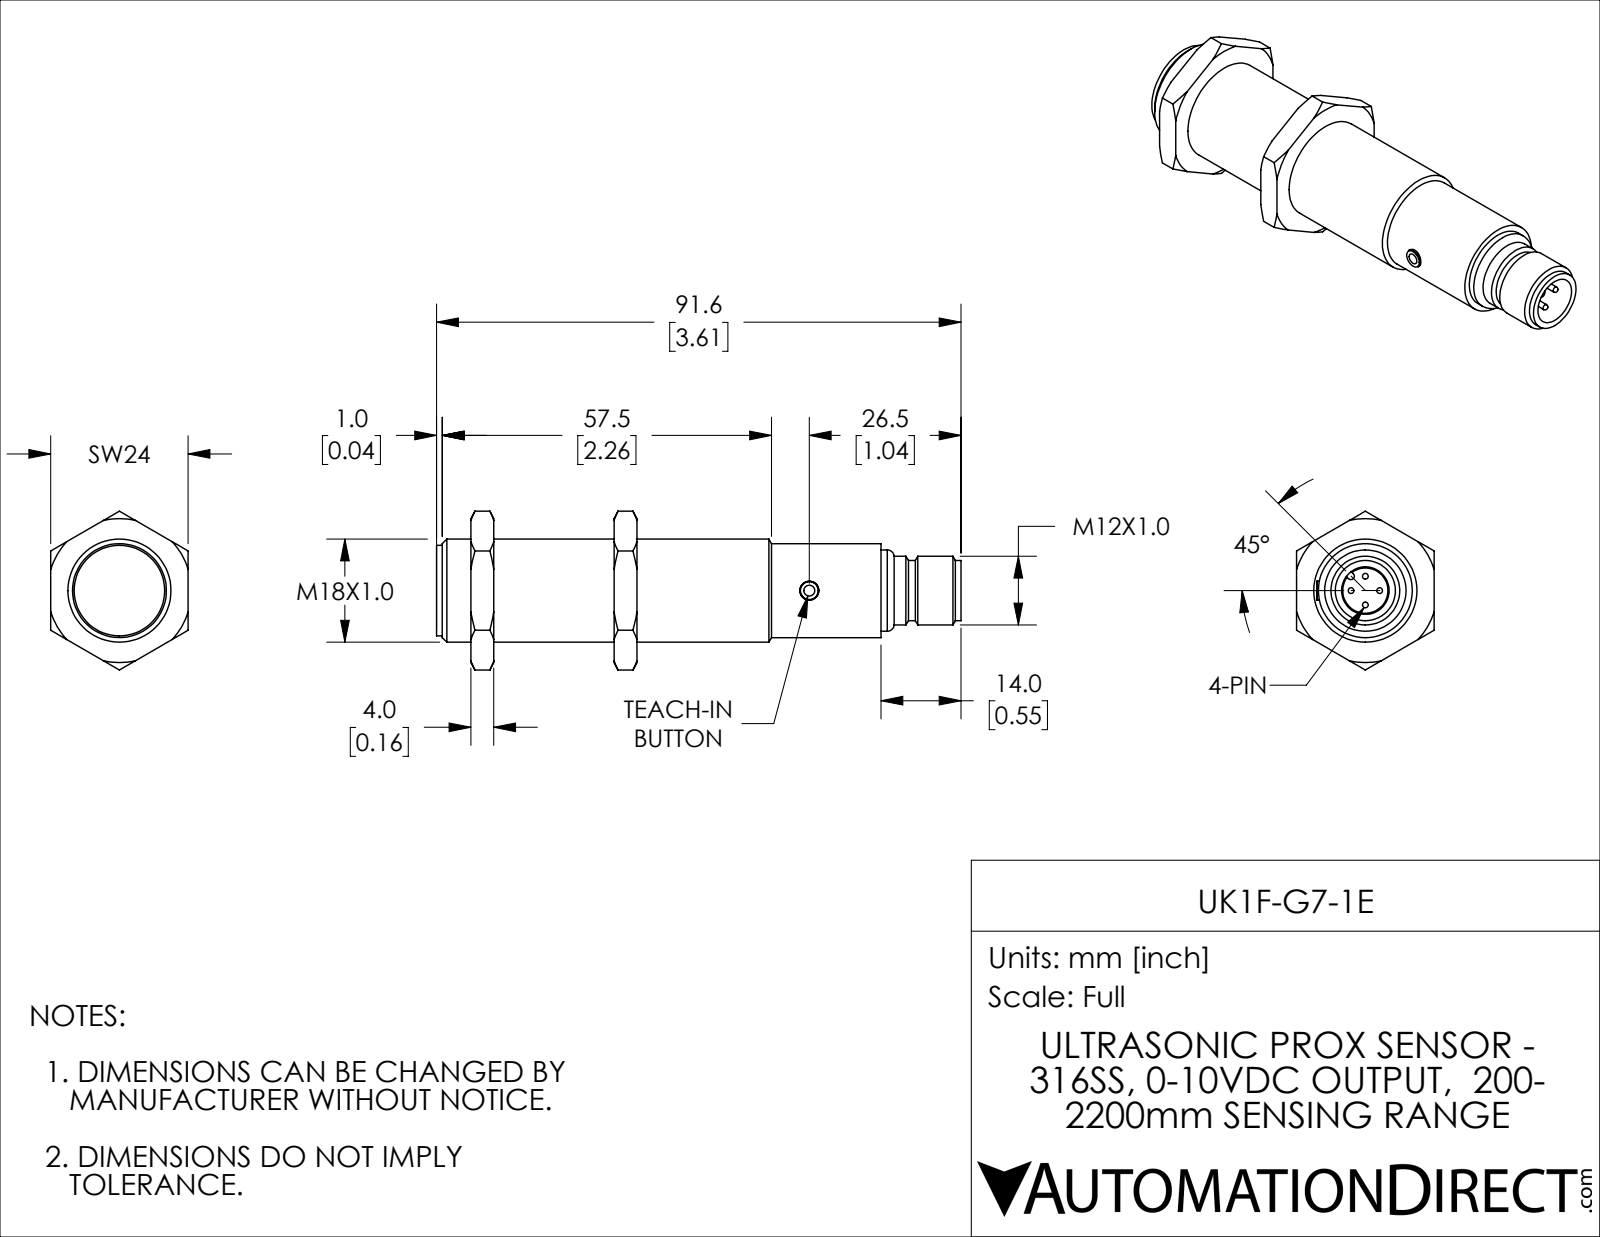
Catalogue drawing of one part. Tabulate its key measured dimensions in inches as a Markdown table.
| quantity | value |
| --- | --- |
| part name | UK1F-G7-1E |
| STEP written by | SolidWorks 2018 (AUTOMOTIVE_DESIGN) |
| units | inches |
| bodies | 4 solids, 113 faces (27 planar, 35 cylindrical, 51 other) |
| overall size | 3.606 × 1.091 × 0.945 |
| volume | 1.338 in³ |
| surface area | 11.97 in² |
| round holes (diameter × count) | 0.13 × 1, 0.327 × 1, 0.709 × 1 |
| round bosses / shafts (diameter × count) | 0.039 × 4, 0.646 × 1, 0.622 × 1, 0.559 × 1, 0.472 × 1, 0.413 × 1 |
| partial cylindrical surfaces (radius × count) | 0.024 × 1 |
| main face-to-face distances | 0.984, 0.157, 0.945, 1.142, 0.827, 0.236, 0.394, 1.22, 1.378, 3.055 |
